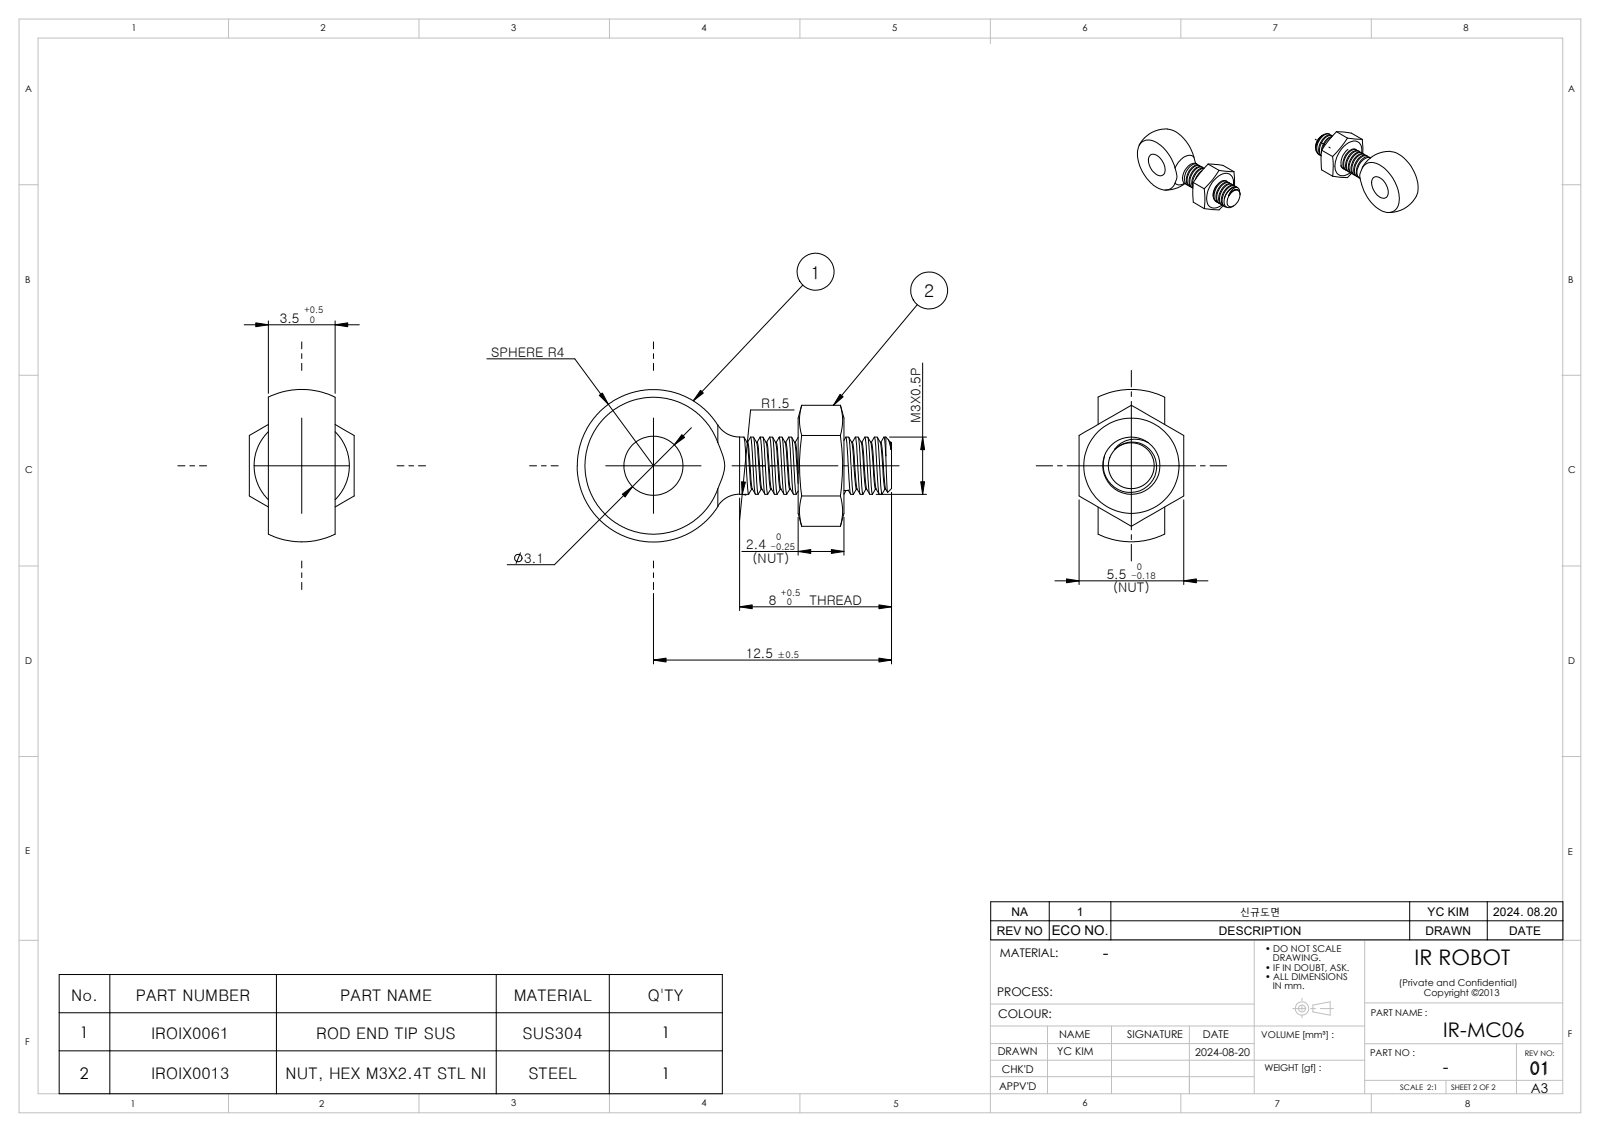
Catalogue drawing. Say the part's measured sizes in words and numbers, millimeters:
The part is named "IROIX0013 NUT, M3.0-2.4T NI; IROIX0061 ROD END TIP SUS, IR-MC06; IR-MC06". Its 3-D file was written by "SolidWorks 2020 (CONFIG_CONTROL_DESIGN)". It is 2 solids with 77 faces: 14 planar, 44 cylindrical and 19 other. Overall it measures 16.5 by 8 by 5.5 millimeters. Its volume is 245 cubic millimeters and its surface area 419 square millimeters. Round holes: 1 of diameter 2.6, 1 of diameter 3.1. Round bosses or shafts: 1 of diameter 3. The main face-to-face distances are 3.5, 5.5, 2.4, 1, 4.5, 2.5, 4.9, 2.75, 1.75.
